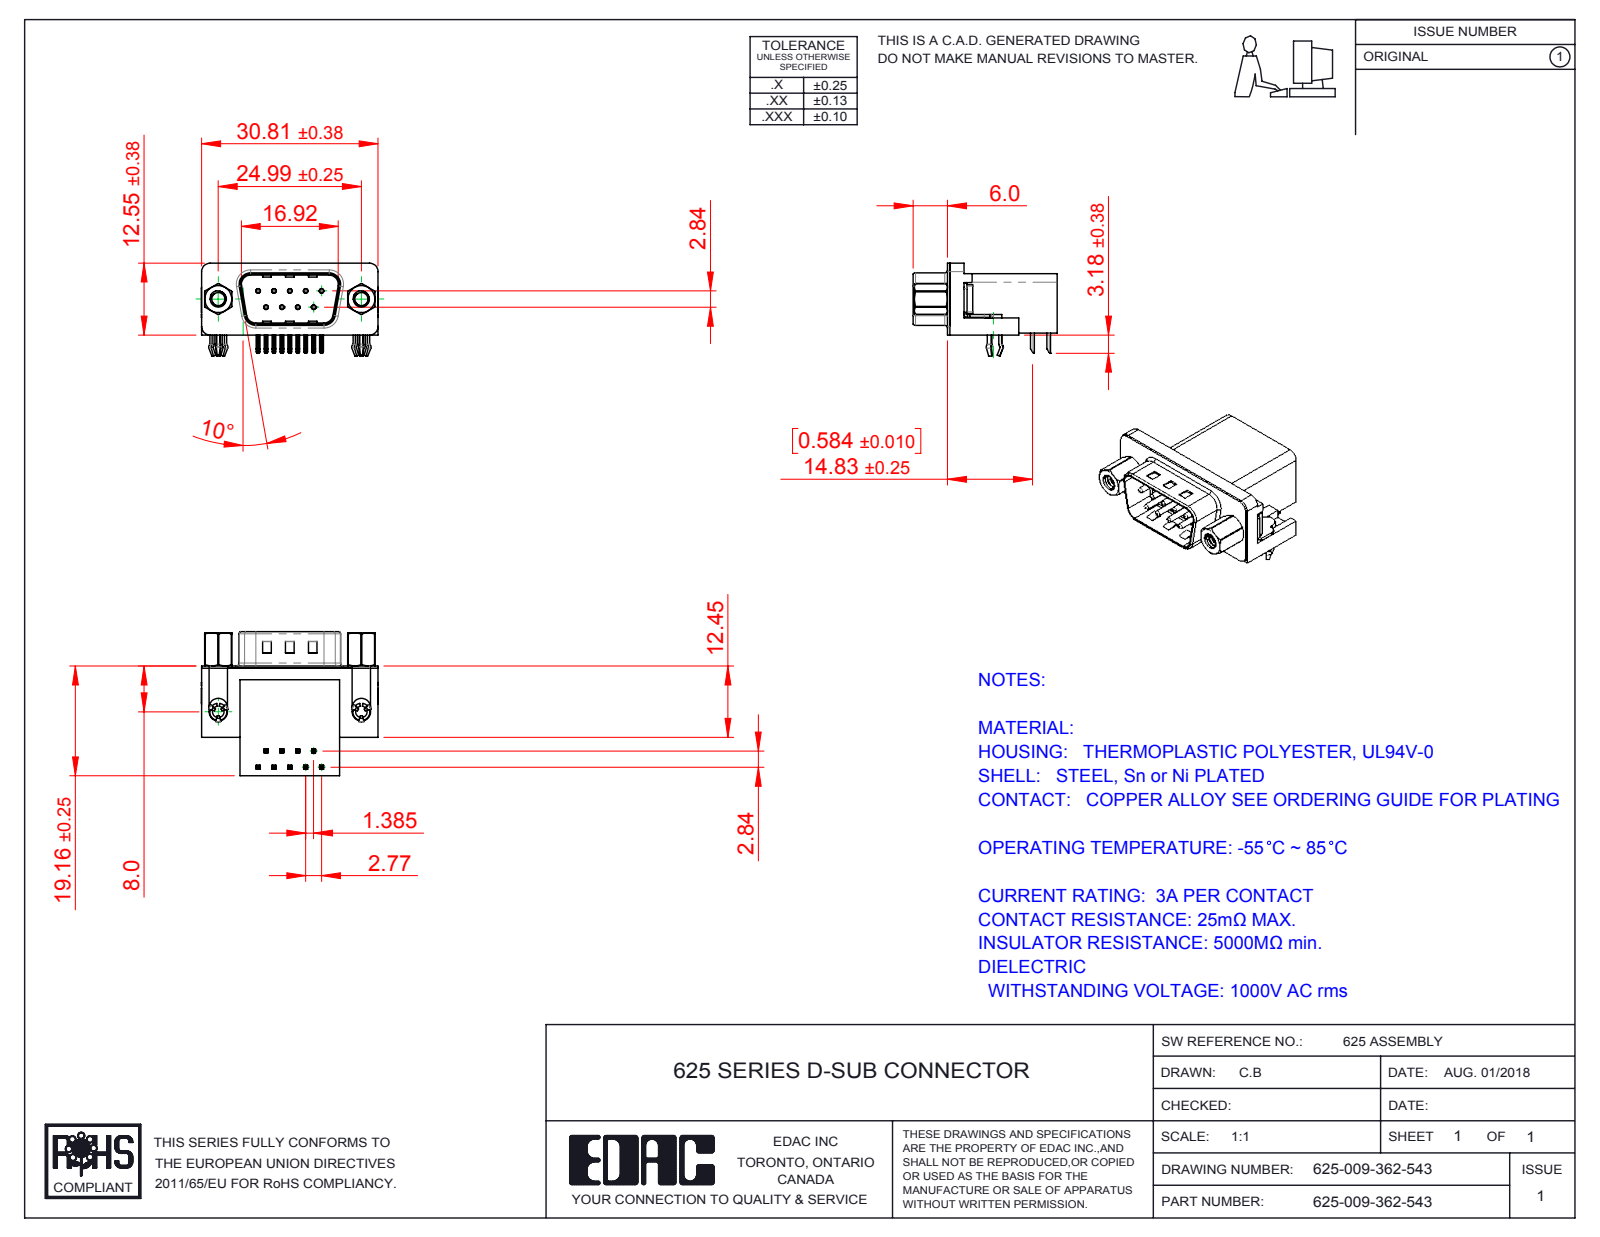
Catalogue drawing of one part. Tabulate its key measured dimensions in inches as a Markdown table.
| quantity | value |
| --- | --- |
| part name | 625 4-40 Threaded Rivet; 625 3 Prong Board Lock; 625 Contact Top; 625 Contact Bottom (+4 more) |
| STEP written by | SolidWorks 2016 (CONFIG_CONTROL_DESIGN) |
| units | inches |
| bodies | 17 solids, 1223 faces (633 planar, 395 cylindrical, 195 other) |
| overall size | 1.216 × 0.991 × 0.64 |
| volume | 0.287 in³ |
| surface area | 8.517 in² |
| round holes (diameter × count) | 0.014 × 9, 0.031 × 9, 0.079 × 2, 0.089 × 2, 0.09 × 2, 0.157 × 2, 0.189 × 2, 0.197 × 2 |
| round bosses / shafts (diameter × count) | 0.03 × 9, 0.193 × 2, 0.187 × 2, 0.154 × 2, 0.118 × 2, 0.11 × 2 |
| partial cylindrical surfaces (radius × count) | 0.01 × 48, 0.005 × 18, 0.039 × 16, 0.02 × 9, 0.059 × 8, 0.063 × 8, 0.035 × 4, 0.079 × 4 |
| main face-to-face distances | 0.016, 0.407, 0.739, 0.754, 0.64, 0.098, 0.114, 0.014, 0.421, 0.264 |
| hole center spacings | 0.124, 0.109, 0.218, 0.198, 0.198, 0.327, 0.294, 0.295 |
